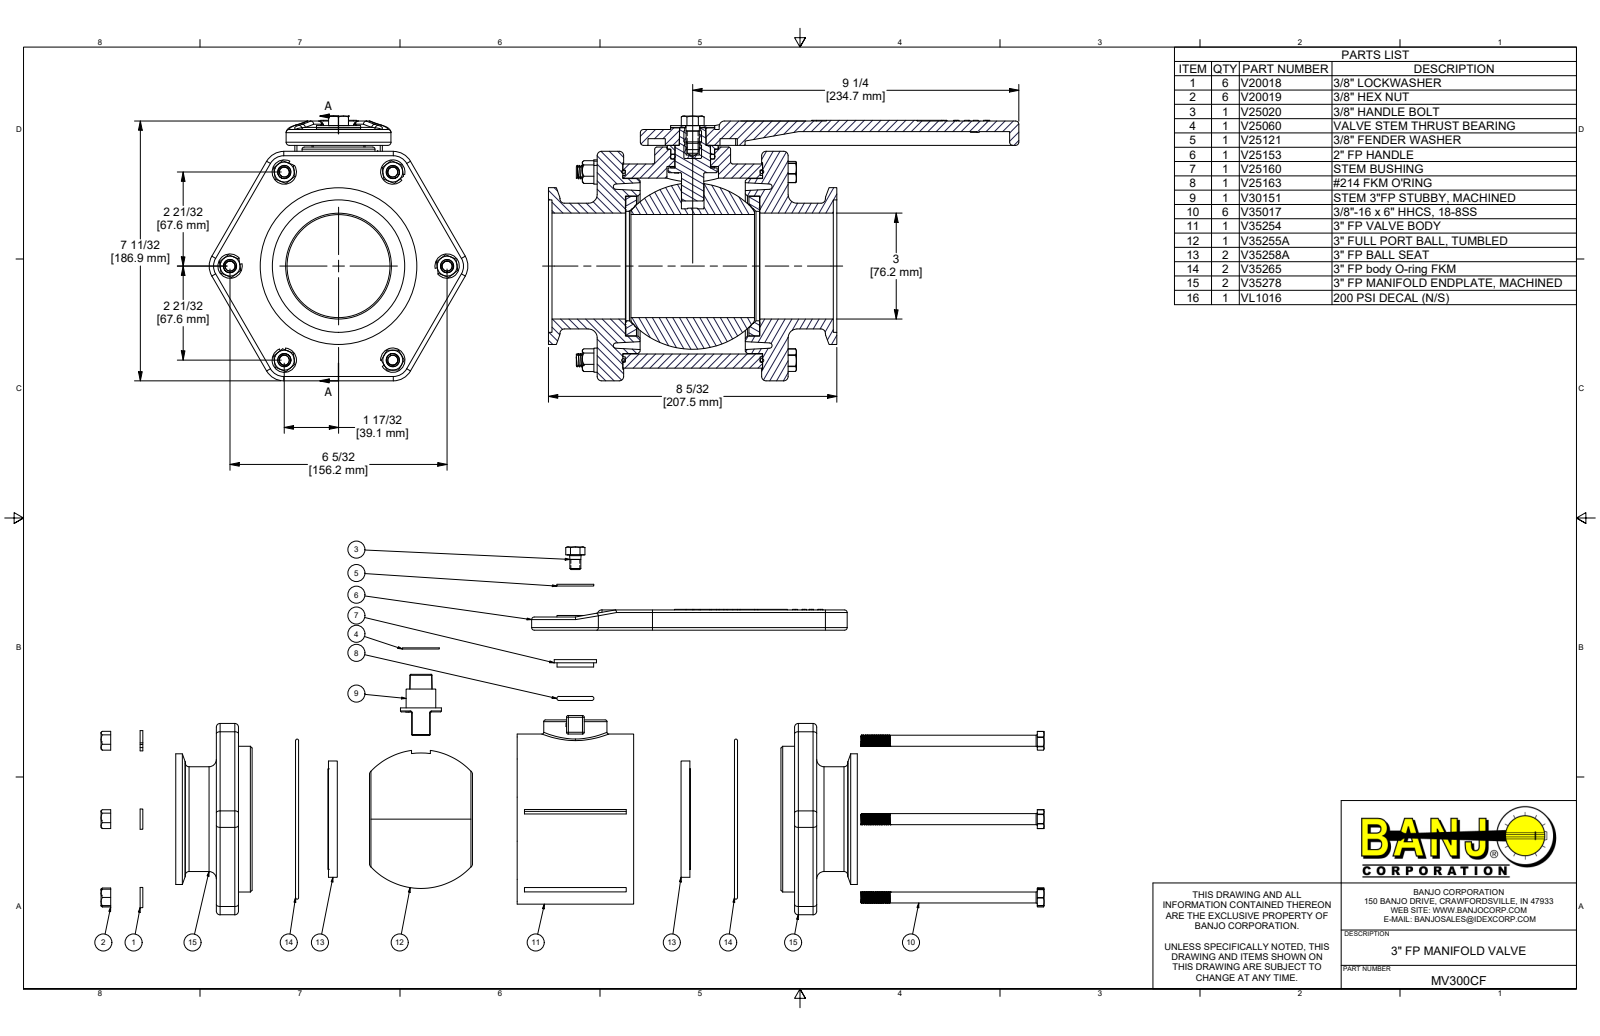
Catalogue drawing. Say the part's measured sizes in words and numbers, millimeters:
The part is named "MV300CF; V35254; VL1000; V35278 (+8 more)". Its 3-D file was written by "Autodesk Inventor 2019 (AUTOMOTIVE_DESIGN)". It is 41 solids with 3475 faces: 1795 planar, 538 cylindrical and 1142 other. Overall it measures 338.5 by 190.4 by 186.2 millimeters. Its volume is 2 070 000 cubic millimeters and its surface area 494 800 square millimeters. Round holes: 12 of diameter 4.3, 8 of diameter 11.2, 6 of diameter 7.2, 6 of diameter 7.8, 6 of diameter 9.8, 1 of diameter 7.8, 1 of diameter 9.5, 1 of diameter 10.3, 1 of diameter 17.3, 1 of diameter 24.4, 1 of diameter 25.4, 1 of diameter 25.8. Round bosses or shafts: 6 of diameter 17.4, 6 of diameter 9.5, 1 of diameter 146.8, 1 of diameter 130.5, 1 of diameter 125.8, 1 of diameter 112.8, 1 of diameter 100.3, 1 of diameter 90.4. Partial cylindrical surfaces (rounded edges, fillets, slot ends): 24 of radius 3.2, 16 of radius 1.5, 10 of radius 0.8, 8 of radius 2.3, 6 of radius 8.1, 6 of radius 14.3, 2 of radius 1.5, 2 of radius 2.1. The main face-to-face distances are 18.4, 119, 137.4, 1.3, 19.1, 20.3, 118.4, 0.6, 99.9, 117.1. The hole center spacings are 57.5, 71.2, 20.7, 78.1, 118.5, 137.6, 138, 36.9.
